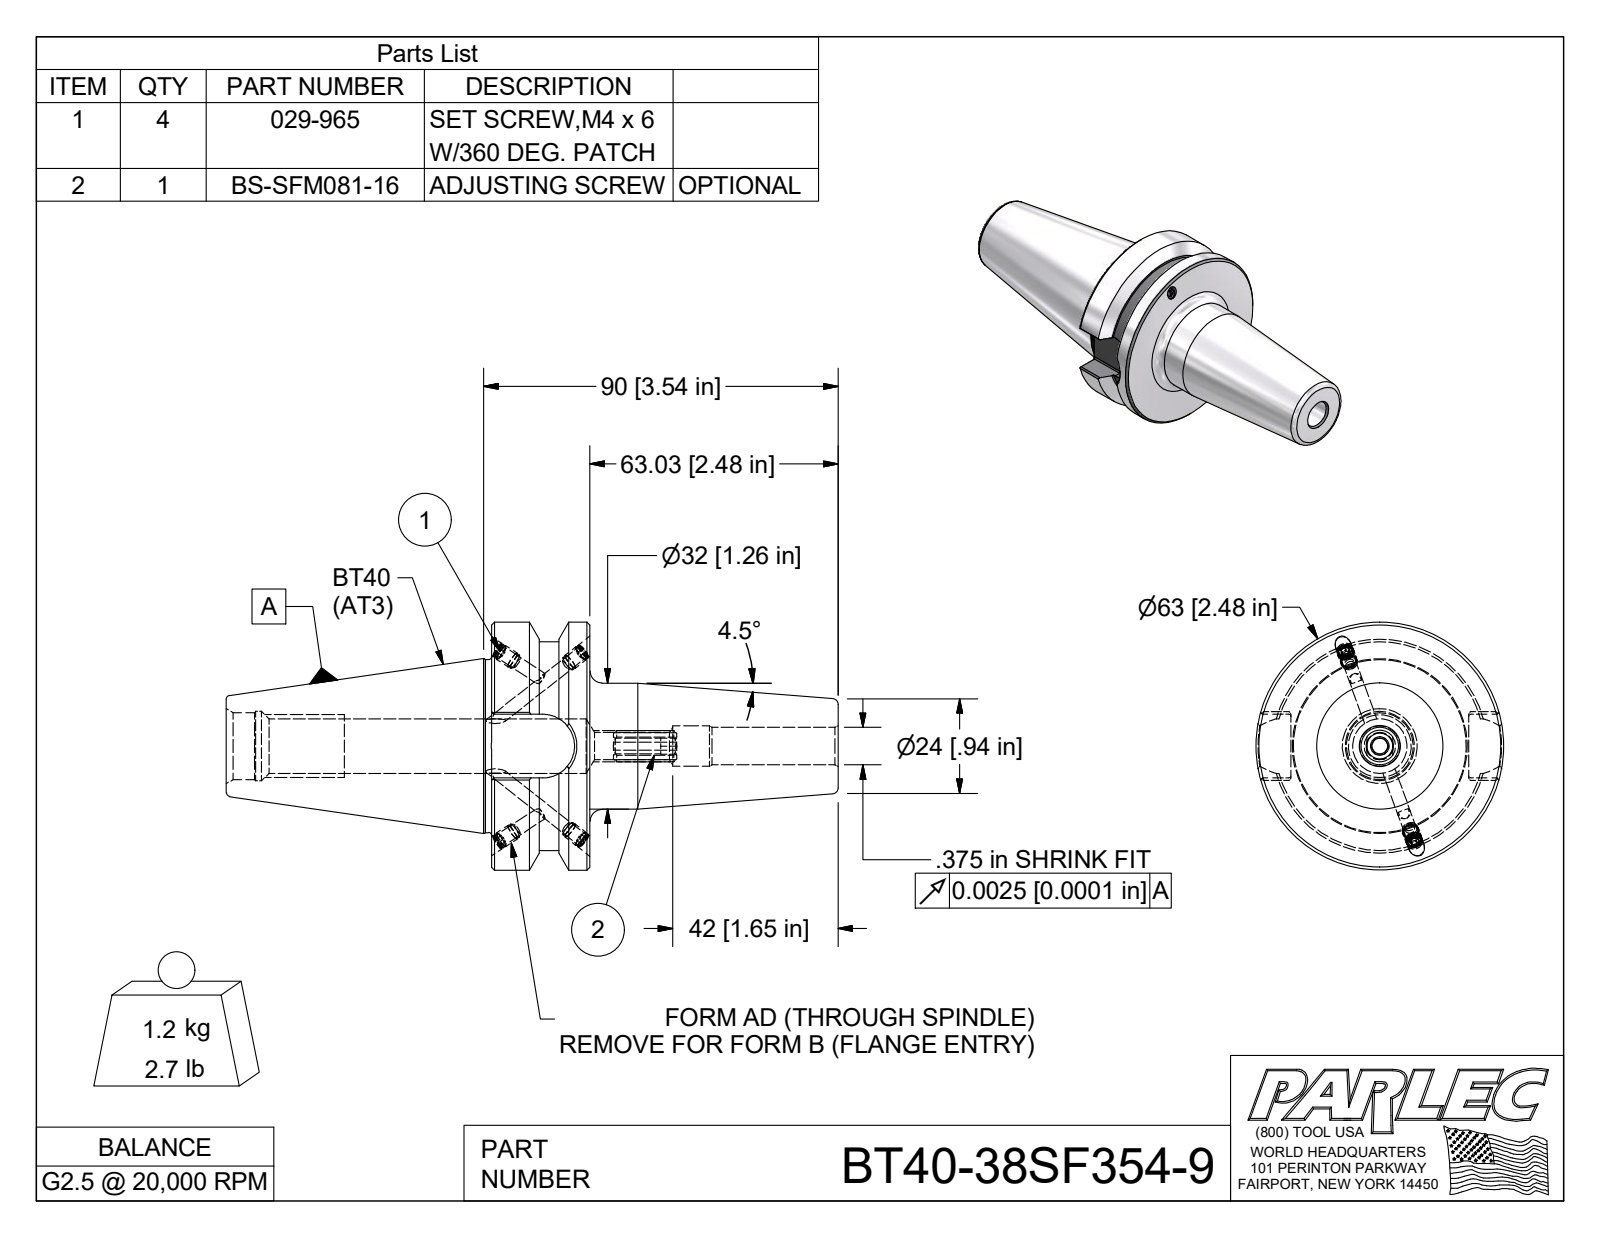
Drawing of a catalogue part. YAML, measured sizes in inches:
part_name: "BT40-38SF354-9; BT40BC-38SF354-9-1; 029-965; BS-SFM081-16"
step_written_by: "Autodesk Inventor 2009 (AUTOMOTIVE_DESIGN)"
units: inches
bodies: {solids: 6, faces: 173, planar: 79, cylindrical: 43, other: 51}
overall_size: [6.118, 2.48, 2.48]
volume: 9.575
surface_area: 48.6
round_holes:
  - {diameter: 0.13, count: 4}
  - {diameter: 0.161, count: 4}
  - {diameter: 0.374, count: 1}
  - {diameter: 0.404, count: 1}
  - {diameter: 0.694, count: 1}
round_bosses_or_shafts:
  - {diameter: 0.165, count: 4}
  - {diameter: 0.157, count: 4}
  - {diameter: 2.48, count: 1}
  - {diameter: 2.087, count: 1}
  - {diameter: 1.75, count: 1}
  - {diameter: 1.73, count: 1}
  - {diameter: 1.26, count: 1}
partial_cylinders:
  - {radius: 0.02, count: 8}
  - {radius: 0.157, count: 1}
  - {radius: 0.319, count: 1}
face_to_face_distances: [0.984, 1.78, 3.465, 2.481, 2.653, 3.637, 6.119, 0.637, 0.762, 1.018]
